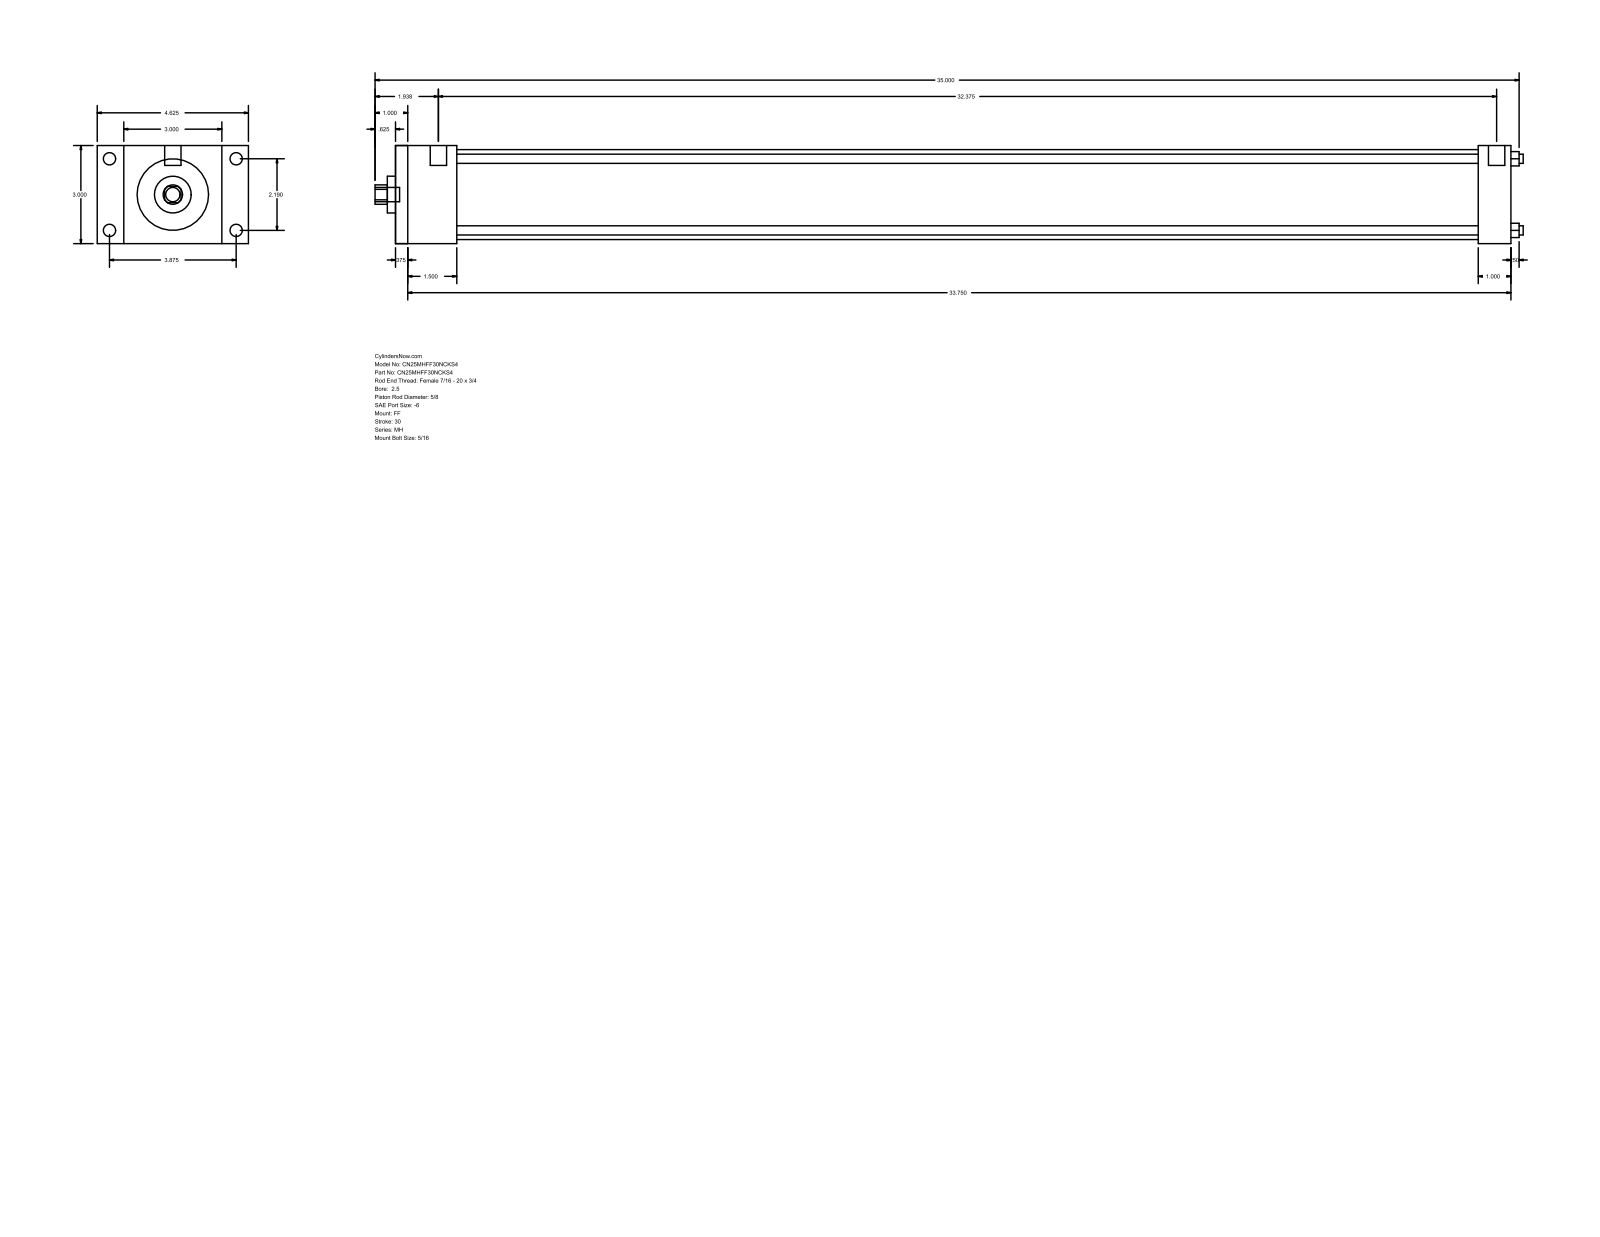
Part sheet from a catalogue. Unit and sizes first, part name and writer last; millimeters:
Units: millimetres
Overall size (bounding box): 892.17 × 117.47 × 76.2
Round holes (diameter × count): ⌀7.14 ×4, ⌀15.88 ×1, ⌀28.57 ×1, ⌀69.85 ×1
Round bosses / shafts (diameter × count): ⌀9.53 ×4, ⌀5.56 ×4, ⌀12.7 ×2, ⌀11.11 ×1
Partial cylindrical surfaces — rounded edges, fillets, slot ends (radius × count): R7.54 ×1
Main face-to-face distances: 76.2, 866.77, 9.52, 857.25, 25.4, 47.62, 841.37, 38.1, 831.85, 793.75
Hole centre spacings: 39.33, 55.62, 78.66
Bodies: 0 solids, 92 faces (64 planar, 28 cylindrical, 0 other)
Part name (STEP PRODUCT): MH_FF__0250_0.625
STEP written by: GSSL Pune (CONFIG_CONTROL_DESIGN)
